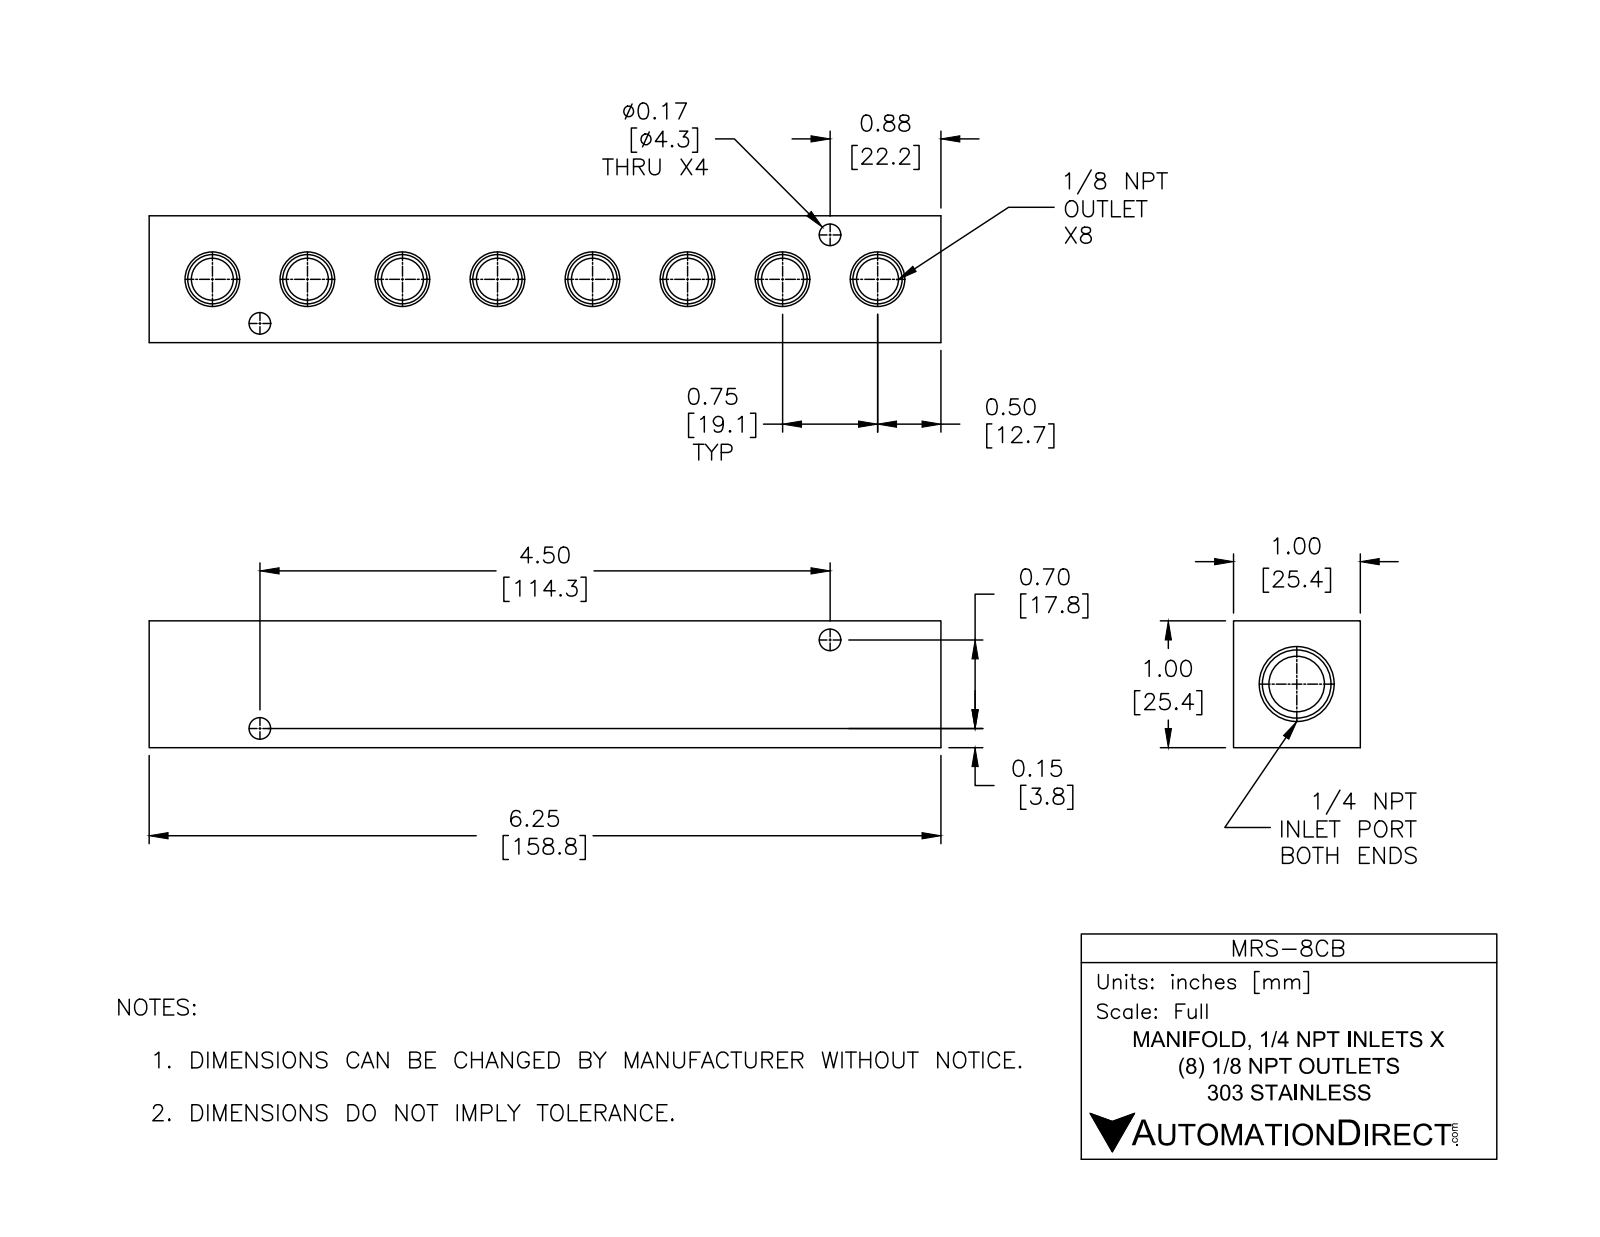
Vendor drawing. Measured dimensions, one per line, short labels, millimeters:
name: MRS-8CB
written by: SolidWorks 2015 (CONFIG_CONTROL_DESIGN)
unit: mm
bodies: 1 solid, 89 faces (16 planar, 33 cylindrical, 40 other)
size: 158.8 × 25.4 × 25.4
volume: 79 990 mm³; area: 24 890 mm²
holes: 6× ⌀8.4, 4× ⌀4.3, 1× ⌀11.1
rounds: 2× R4.2
face distances: 25.4, 158.8, 18.5, 6.9, 9.9, 148.8, 138.9
hole spacings: 19.1, 38.1, 57.2, 13, 76.2, 115.7, 29.9, 29.9
